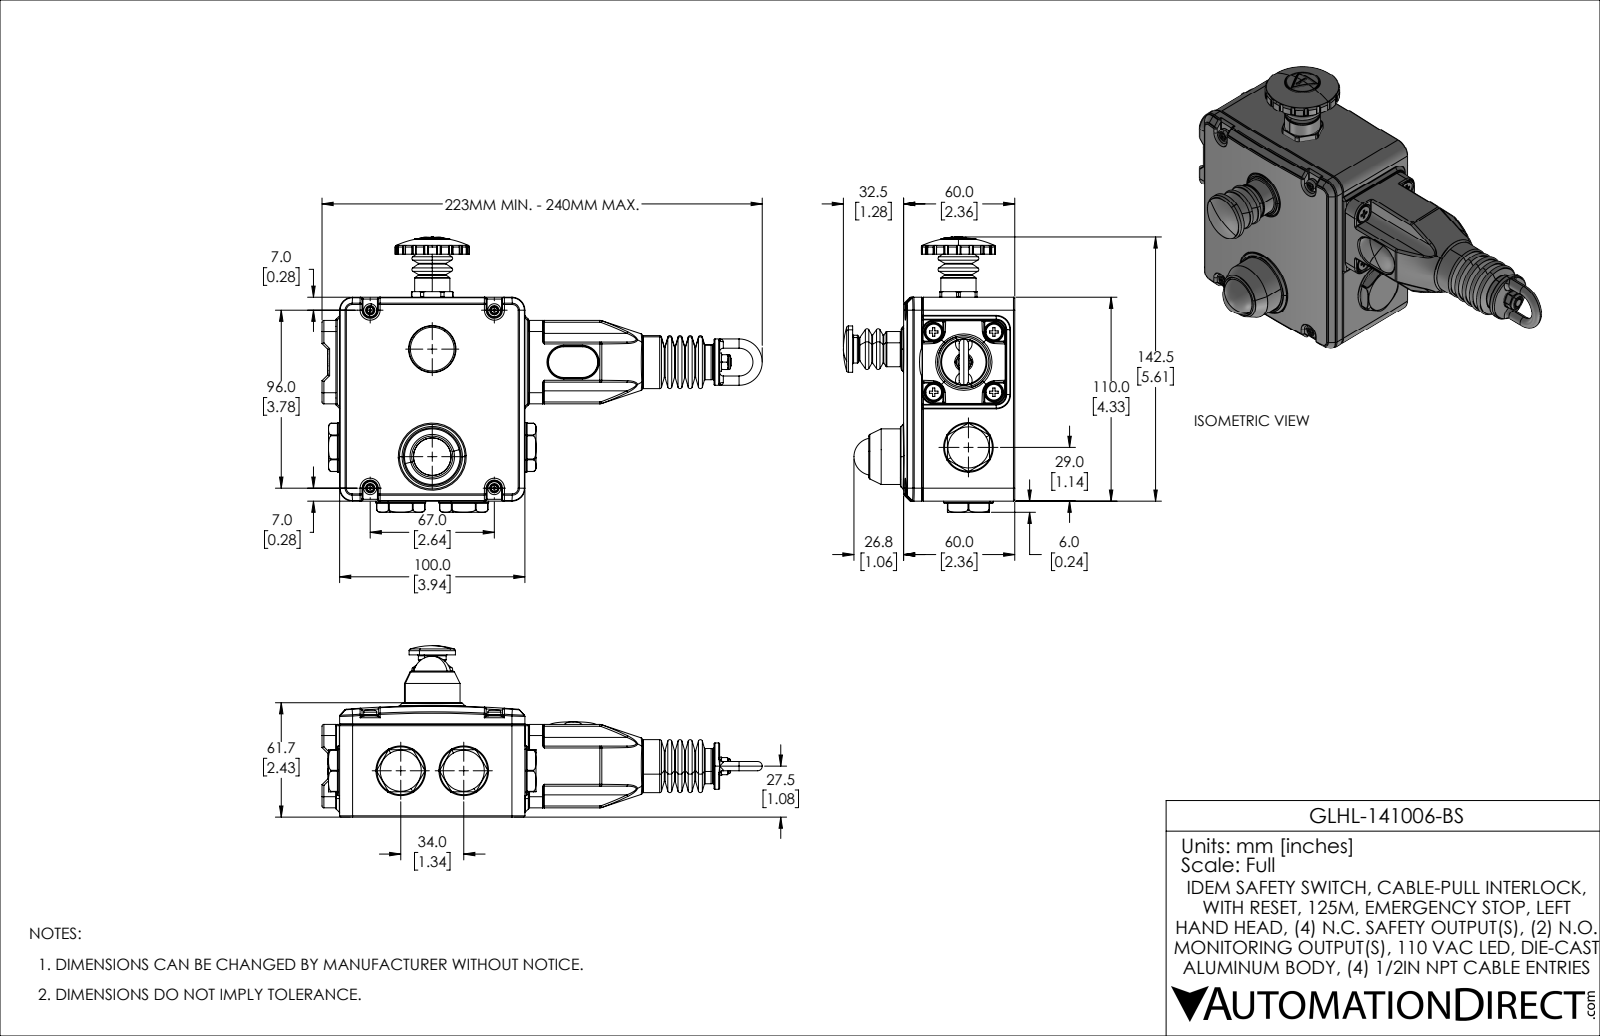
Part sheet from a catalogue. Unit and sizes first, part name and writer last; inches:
Units: inches
Overall size (bounding box): 9.354 × 5.847 × 3.642
Round holes (diameter × count): ⌀0.197 ×11, ⌀0.209 ×9, ⌀0.374 ×7, ⌀0.354 ×6, ⌀0.13 ×4, ⌀0.157 ×4, ⌀0.189 ×4, ⌀0.213 ×4, ⌀0.228 ×4, ⌀0.067 ×3, ⌀0.102 ×3, ⌀0.118 ×3
Round bosses / shafts (diameter × count): ⌀0.335 ×7, ⌀0.236 ×7, ⌀0.173 ×7, ⌀0.197 ×6, ⌀0.276 ×5, ⌀0.138 ×4, ⌀0.051 ×4, ⌀1.055 ×3
Partial cylindrical surfaces — rounded edges, fillets, slot ends (radius × count): R0.02 ×241, R0.039 ×158, R0.008 ×148, R0.028 ×72, R0.012 ×26, R0.006 ×14, R0.004 ×13, R0.236 ×12
Main face-to-face distances: 0.138, 2.157, 0.114, 2.043, 4.331, 0.055, 0.079, 0.157, 4.016, 3.878
Hole centre spacings: 1.28, 0.228, 0.374, 0.905, 1.891, 1.913, 3.012, 3.489
Volume: 18.8 in³ · Surface area: 299.9 in²
Bodies: 43 solids, 4892 faces (1501 planar, 1613 cylindrical, 1778 other)
Part name (STEP PRODUCT): GLHL-141006-AS
STEP written by: SolidWorks 2021 (AUTOMOTIVE_DESIGN)
